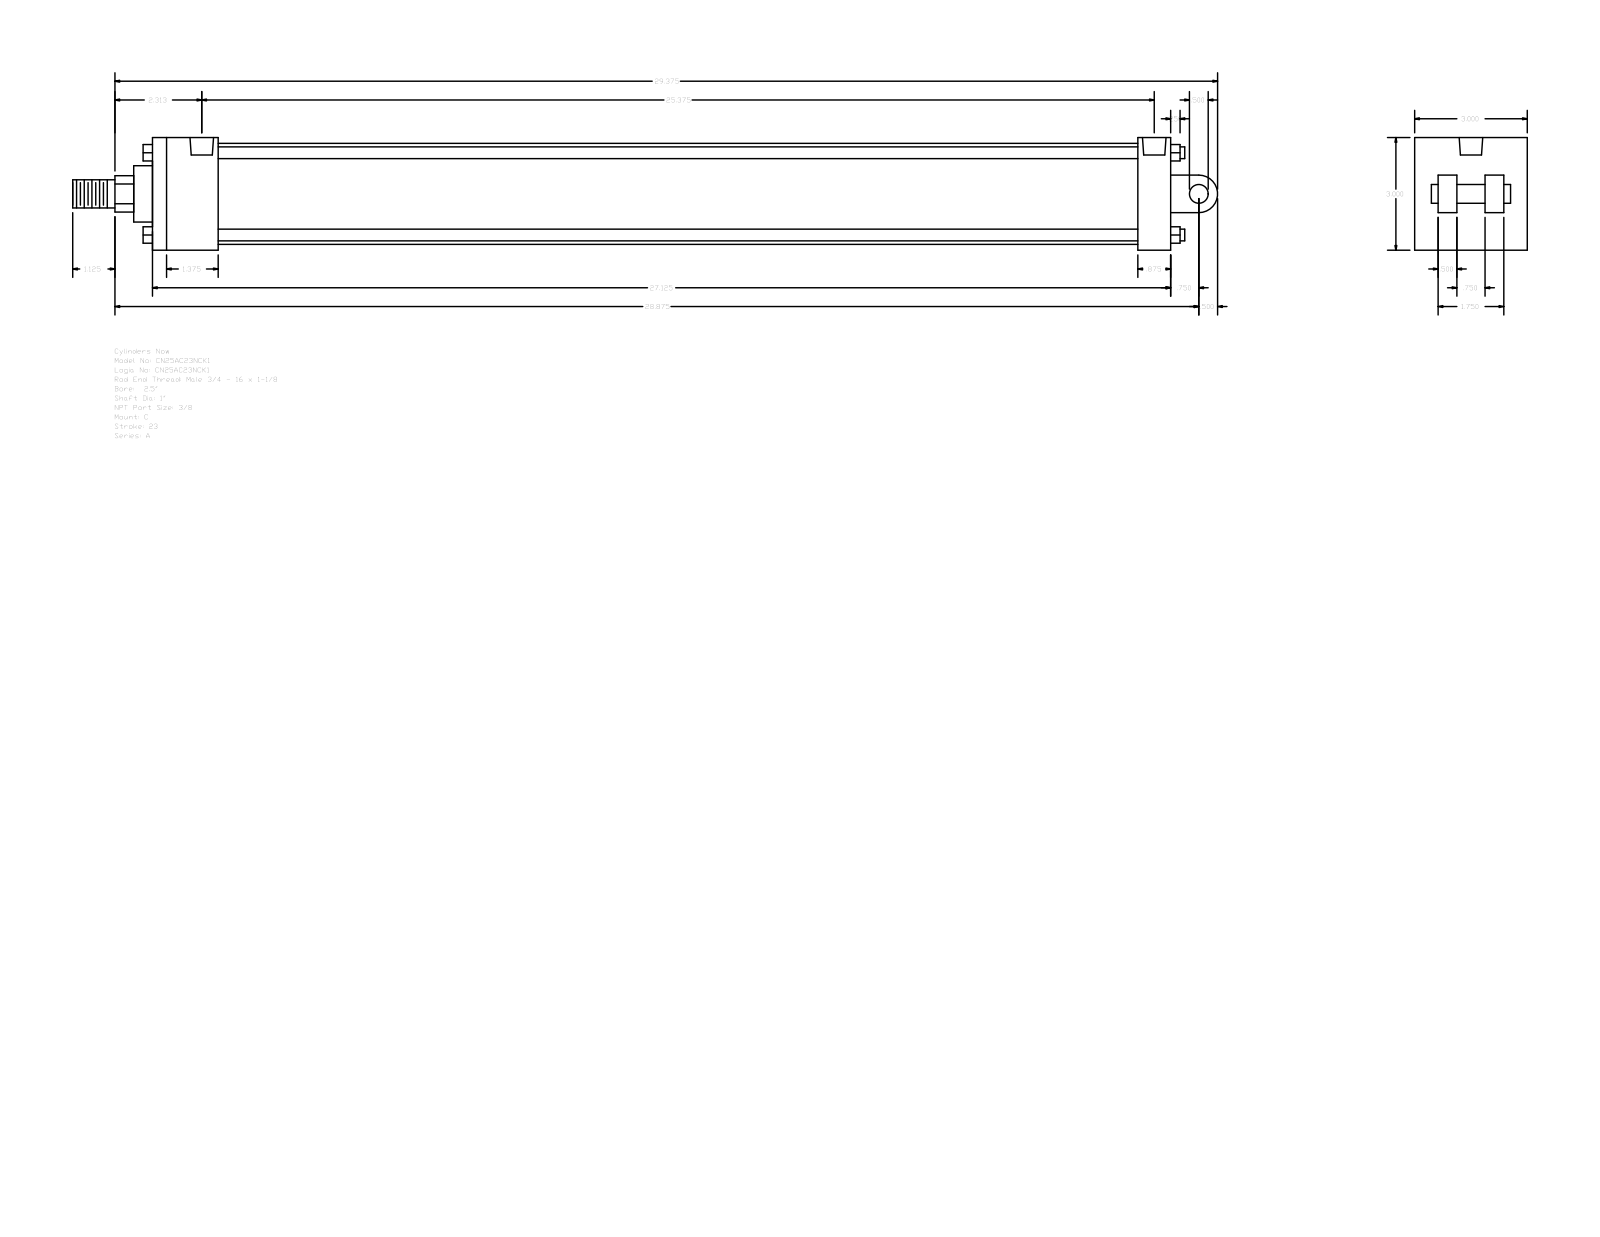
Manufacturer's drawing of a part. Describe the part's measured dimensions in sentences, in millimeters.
The part is named "A_C__0250_1". Its 3-D file was written by "GSSL Pune (CONFIG_CONTROL_DESIGN)". It is 0 solids with 135 faces: 102 planar, 33 cylindrical and 0 other. Overall it measures 774.7 by 76.2 by 76.2 millimeters. Round holes: 4 of diameter 5.56, 2 of diameter 15.93. Round bosses or shafts: 4 of diameter 7.94, 1 of diameter 68.33, 1 of diameter 38.1, 1 of diameter 25.4, 1 of diameter 19.05, 1 of diameter 12.7. Partial cylindrical surfaces (rounded edges, fillets, slot ends): 1 of radius 12.29, 1 of radius 12.7. The main face-to-face distances are 76.2, 688.98, 12.7, 44.45, 666.75, 622.3, 644.53, 22.23, 15.87, 25.4. The hole center spacings are 2.38, 646.9, 649.28, 644.52.
